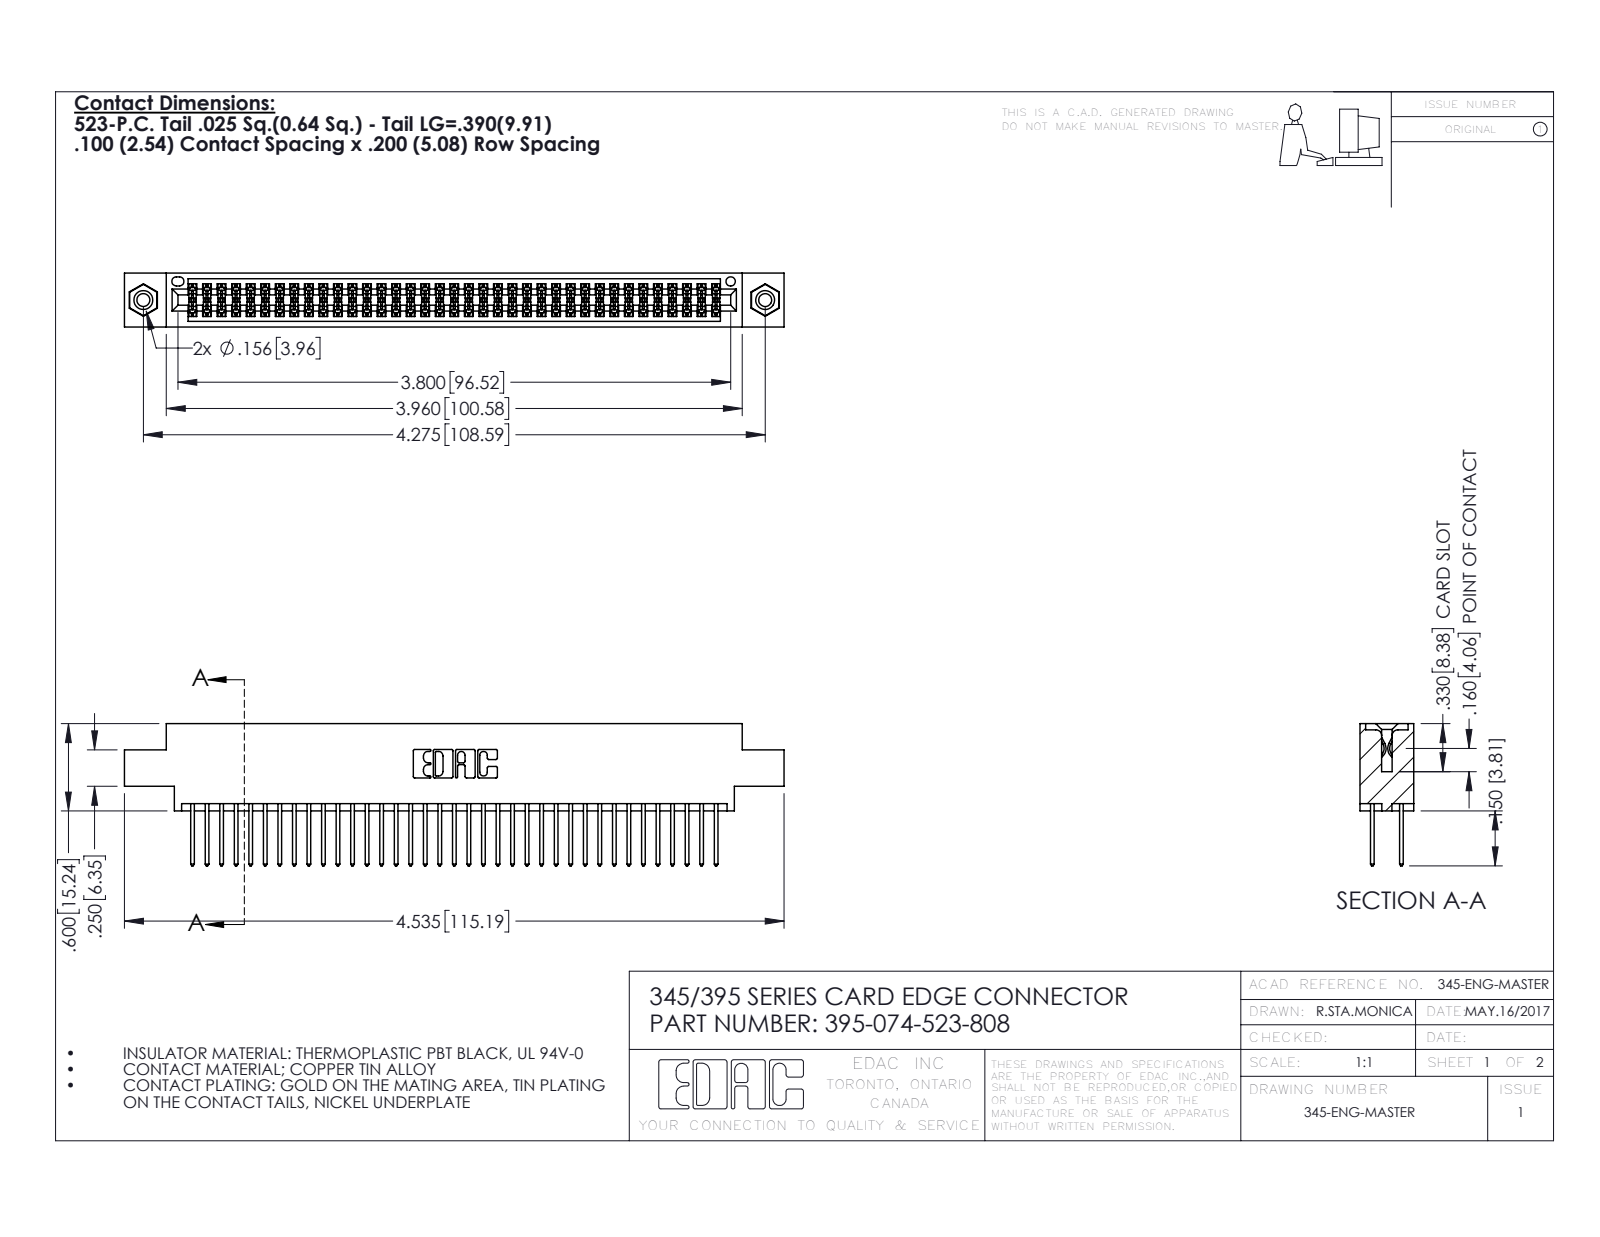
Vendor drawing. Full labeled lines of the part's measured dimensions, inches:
Part name (STEP PRODUCT): 395-074-523-808; 345-292-001_345-293-123; 345 Part_0.170 Offset - 0.156 Dia-TI; 345-250-001_345-250-003-102
STEP written by: SolidWorks 2016 (CONFIG_CONTROL_DESIGN)
Units: inches
Bodies: 77 solids, 3890 faces (2558 planar, 1316 cylindrical, 16 other)
Overall size (bounding box): 4.535 × 0.977 × 0.37
Volume: 0.682 in³ · Surface area: 26.75 in²
Round holes (diameter × count): ⌀0.089 ×2, ⌀0.125 ×2, ⌀0.156 ×2, ⌀0.064 ×1
Round bosses / shafts (diameter × count): ⌀0.155 ×2
Partial cylindrical surfaces — rounded edges, fillets, slot ends (radius × count): R0.006 ×111, R0.01 ×74, R0.01 ×22, R0.007 ×6, R0.031 ×6, R0.026 ×3, R0.014 ×2, R0.019 ×2
Main face-to-face distances: 0.072, 0.298, 0.2, 0.098, 0.272, 0.025, 0.37, 0.225, 0.175, 0.149
Hole centre spacings: 0.27, 4.039, 4.275
